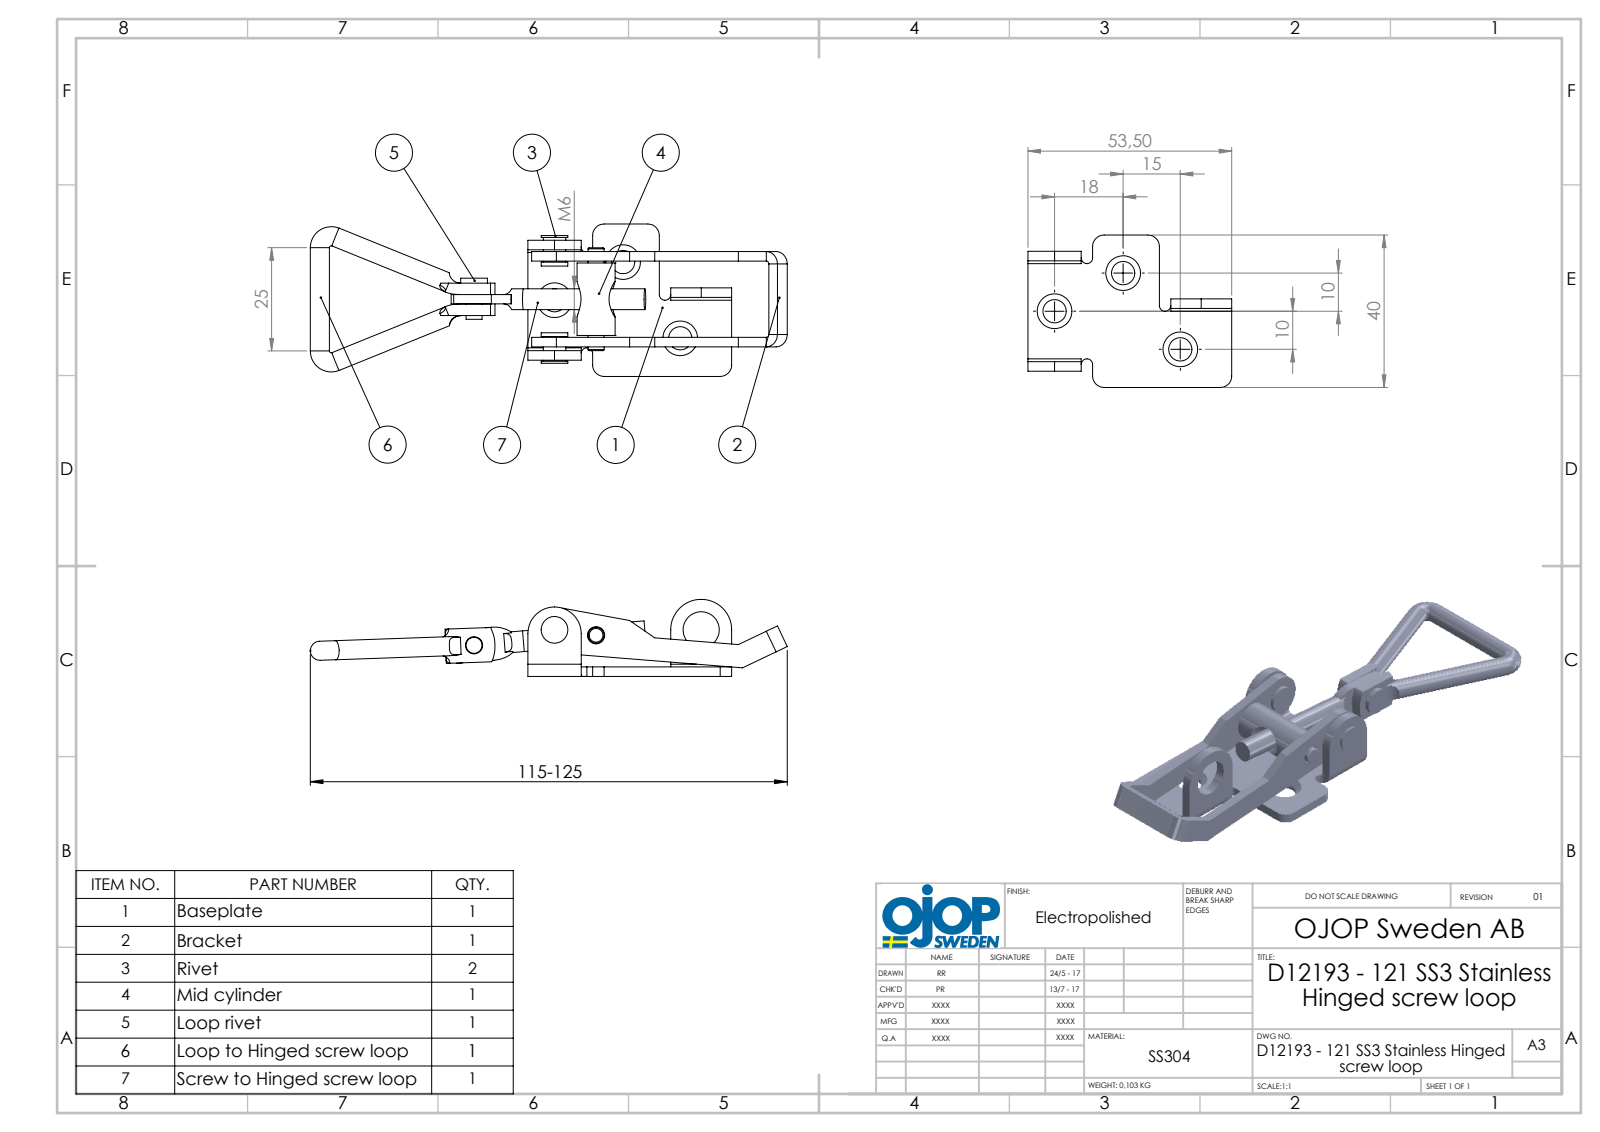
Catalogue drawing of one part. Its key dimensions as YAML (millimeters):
part_name: "rulle; bygel; nit; D12193 (+4 more)"
step_written_by: "SolidWorks 2015 (AUTOMOTIVE_DESIGN)"
units: millimeters
bodies: {solids: 8, faces: 216, planar: 88, cylindrical: 100, other: 28}
overall_size: [125.18, 40, 20.24]
volume: 13436
surface_area: 13163
round_holes:
  - {diameter: 6.1, count: 3}
  - {diameter: 4.5, count: 2}
  - {diameter: 6, count: 2}
  - {diameter: 9.5, count: 1}
round_bosses_or_shafts:
  - {diameter: 5, count: 3}
  - {diameter: 7, count: 2}
  - {diameter: 4.2, count: 2}
  - {diameter: 10, count: 1}
  - {diameter: 5.9, count: 1}
  - {diameter: 5.47, count: 1}
  - {diameter: 5.46, count: 1}
partial_cylinders:
  - {radius: 3, count: 6}
  - {radius: 0.74, count: 5}
  - {radius: 3.24, count: 5}
  - {radius: 1.5, count: 3}
  - {radius: 2, count: 2}
  - {radius: 10, count: 2}
  - {radius: 6, count: 1}
  - {radius: 7, count: 1}
face_to_face_distances: [2.5, 22.5, 25, 20, 6, 12.97, 9.53, 3, 3.5, 16.47]
hole_center_spacings: [11, 20.67, 21.5, 25, 27.63, 32.14, 33.72, 38.5]
